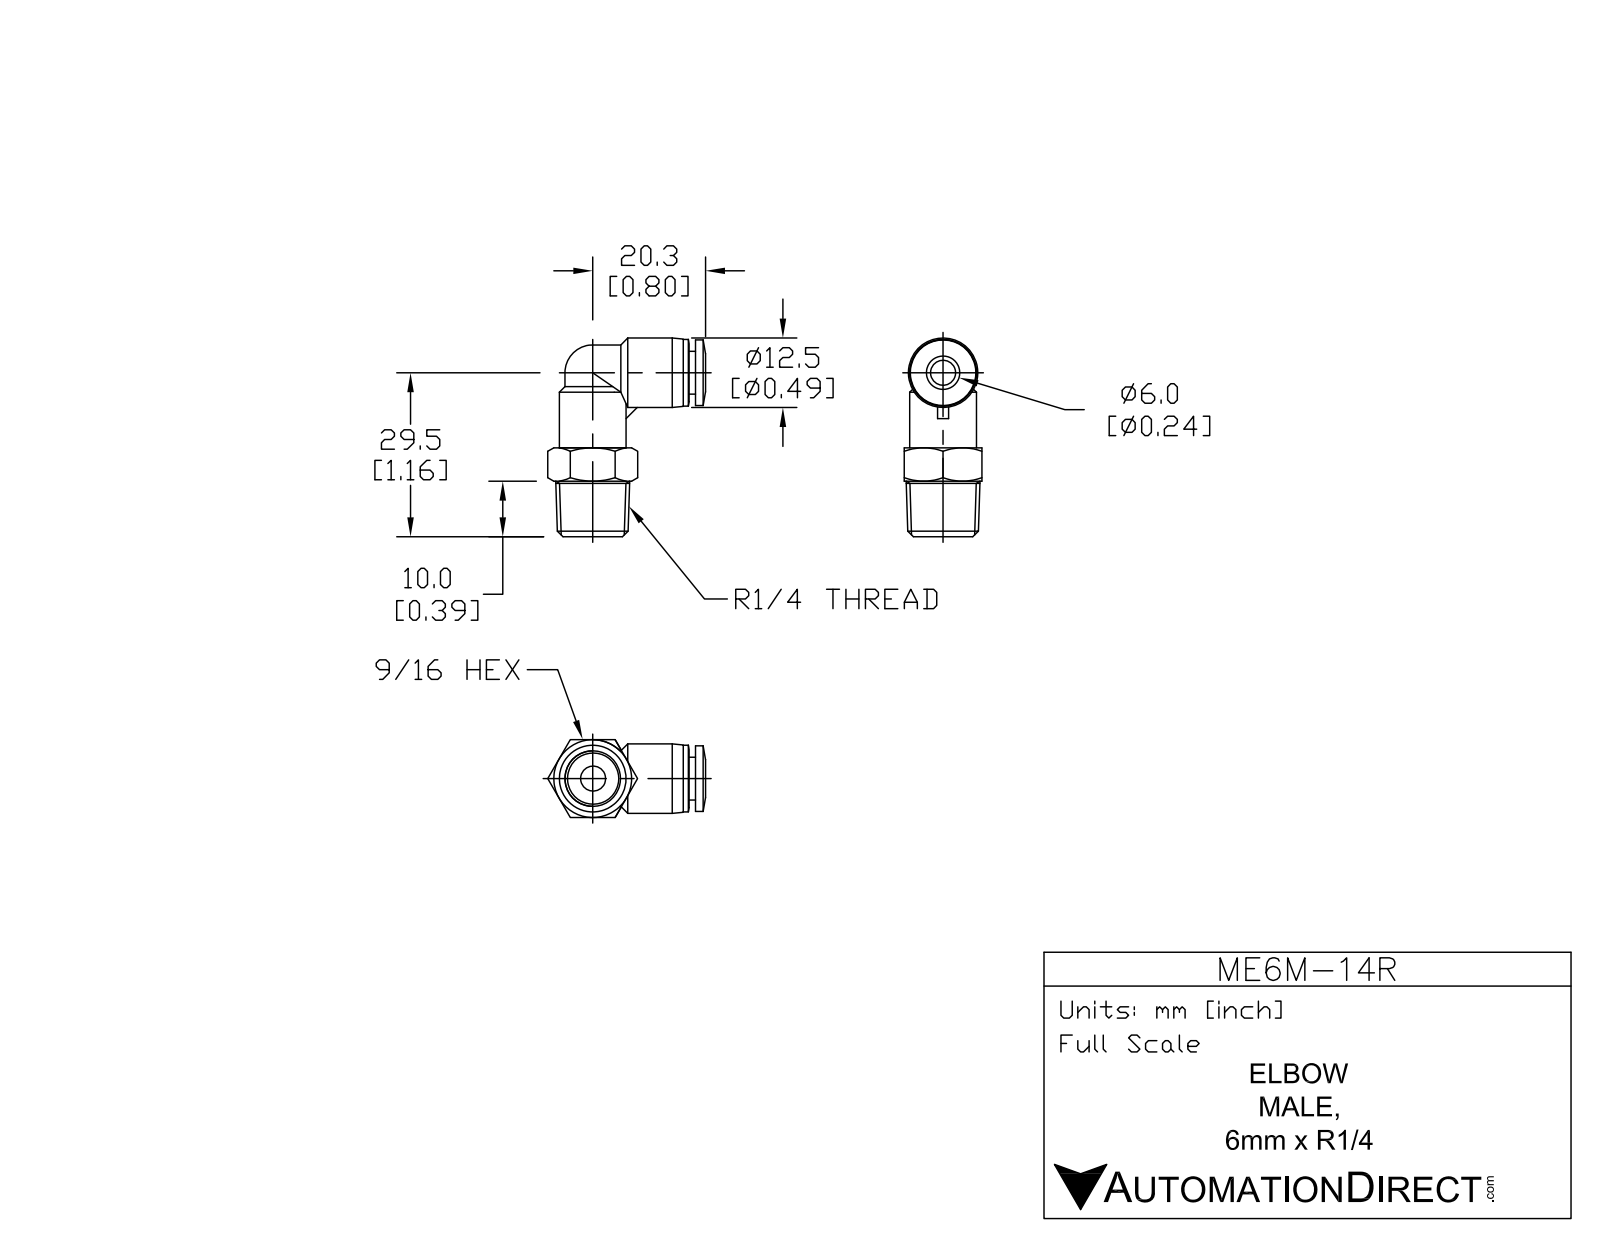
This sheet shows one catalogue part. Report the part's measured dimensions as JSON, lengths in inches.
{"part_name": "ME6M-14R", "step_written_by": "SolidWorks 2015 (AUTOMOTIVE_DESIGN)", "units": "inches", "bodies": {"solids": 1, "faces": 69, "planar": 17, "cylindrical": 19, "other": 33}, "overall_size": [1.407, 1.117, 0.551], "volume_in3": 0.297, "surface_area_in2": 4.68, "round_holes": [[0.157, 2], [0.248, 1]], "round_bosses_or_shafts": [[0.472, 2], [0.492, 1], [0.465, 1], [0.303, 1]], "partial_cylinders_radius": [[0.197, 2]], "face_to_face_distances": [0.551, 0.63, 0.045, 0.236, 0.53, 0.575, 0.394, 0.315, 0.646, 0.116]}
